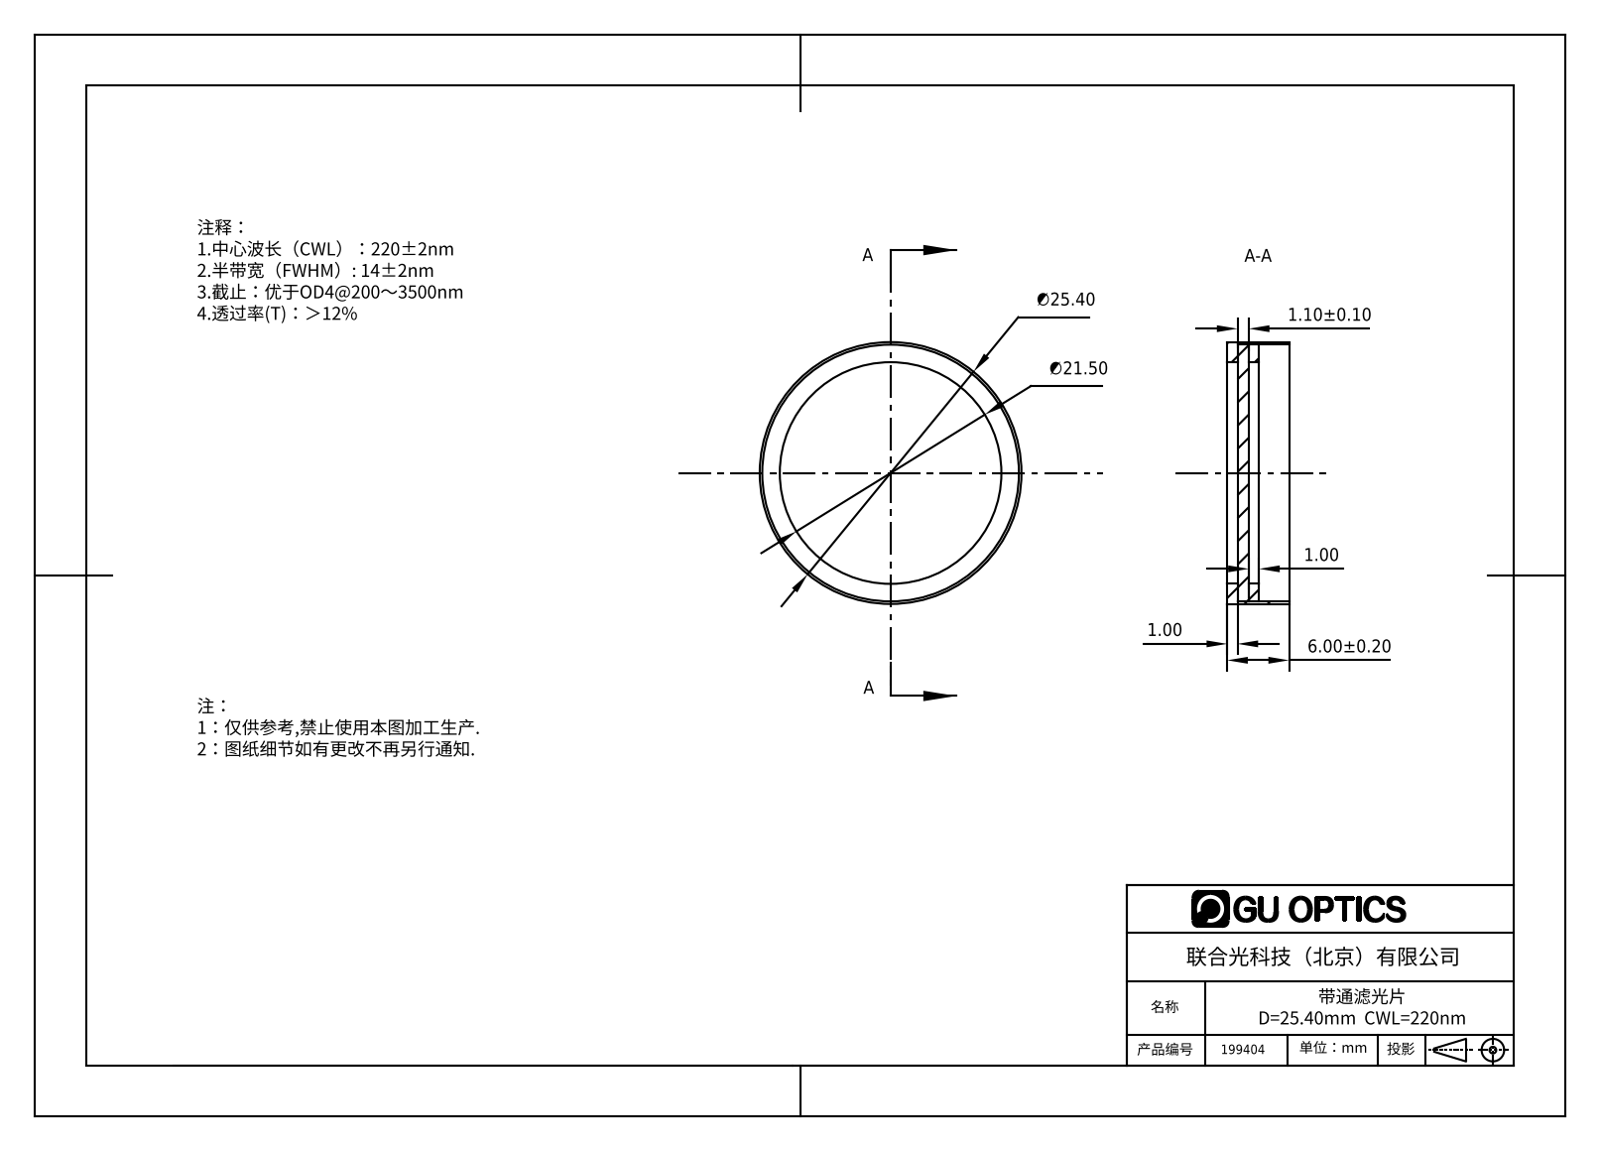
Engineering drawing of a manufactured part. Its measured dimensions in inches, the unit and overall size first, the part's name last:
Units: inches
Overall size (bounding box): 1 × 1 × 0.236
Round holes (diameter × count): ⌀0.846 ×1
Round bosses / shafts (diameter × count): ⌀1 ×1, ⌀0.98 ×1
Main face-to-face distances: 0.043, 0.039, 0.083, 0.122, 0.236, 0.197, 0.154, 0.114
Volume: 0.055 in³ · Surface area: 4.151 in²
Bodies: 3 solids, 19 faces (7 planar, 12 cylindrical, 0 other)
Part name (STEP PRODUCT): 198750
STEP written by: SolidWorks 2019 (AUTOMOTIVE_DESIGN)
